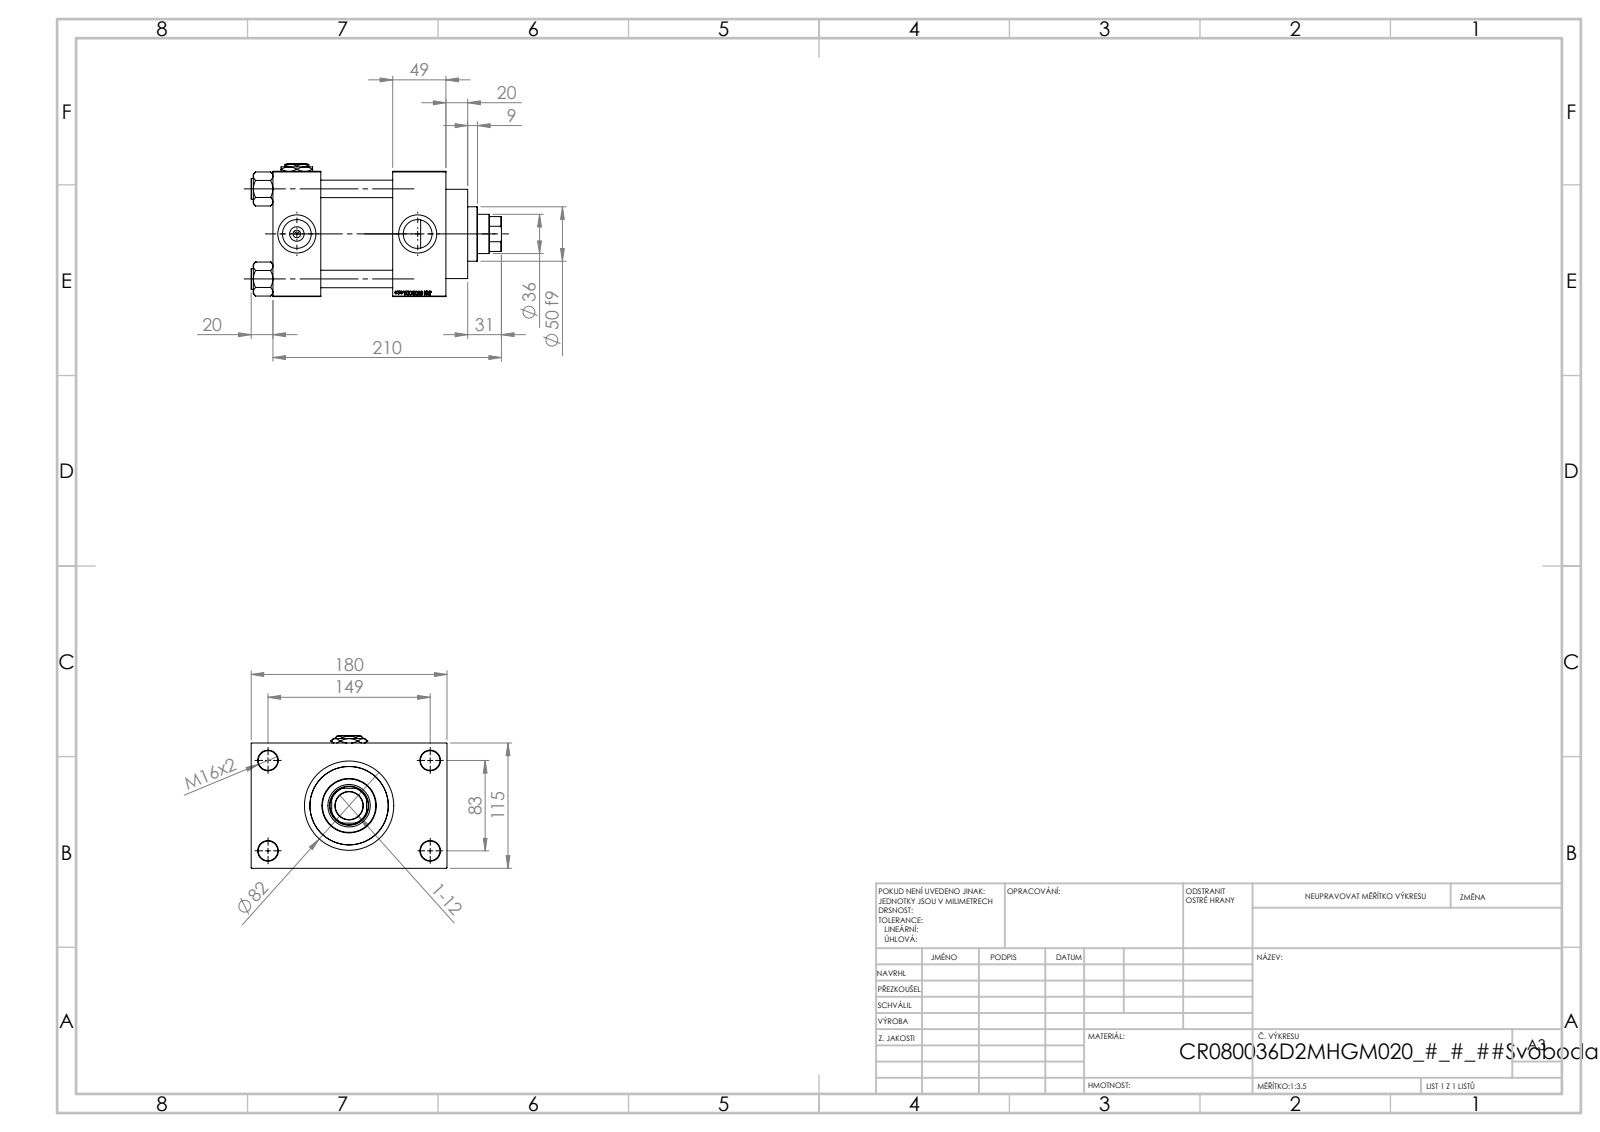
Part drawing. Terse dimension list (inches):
name: V215_VC_A; V215CR_D_TYCINKA; V215CR_VCP_D; Zatka_pro_OIL_PORT (+2 more)
written by: SolidWorks 2019 (CONFIG_CONTROL_DESIGN)
unit: in
bodies: 12 solids, 1204 faces (569 planar, 95 cylindrical, 540 other)
size: 9.055 × 7.087 × 4.803
volume: 120.6 in³; area: 465.6 in²
holes: 4× ⌀0.63, 4× ⌀0.709, 3× ⌀0.276, 3× ⌀1.041, 3× ⌀1.378, 1× ⌀1.004, 1× ⌀1.417, 1× ⌀1.535, 1× ⌀2.402, 1× ⌀2.835, 1× ⌀3.15
bosses: 4× ⌀0.748, 1× ⌀3.386, 1× ⌀3.228, 1× ⌀1.969
rounds: 1× R0.689
face distances: 4.528, 2.598, 4.331, 1.929, 1.732, 6.26, 1.28, 5.807, 0.787, 2.717
hole spacings: 1.305, 2.302, 3.256, 3.357, 3.513, 4.561, 5.607, 3.268
